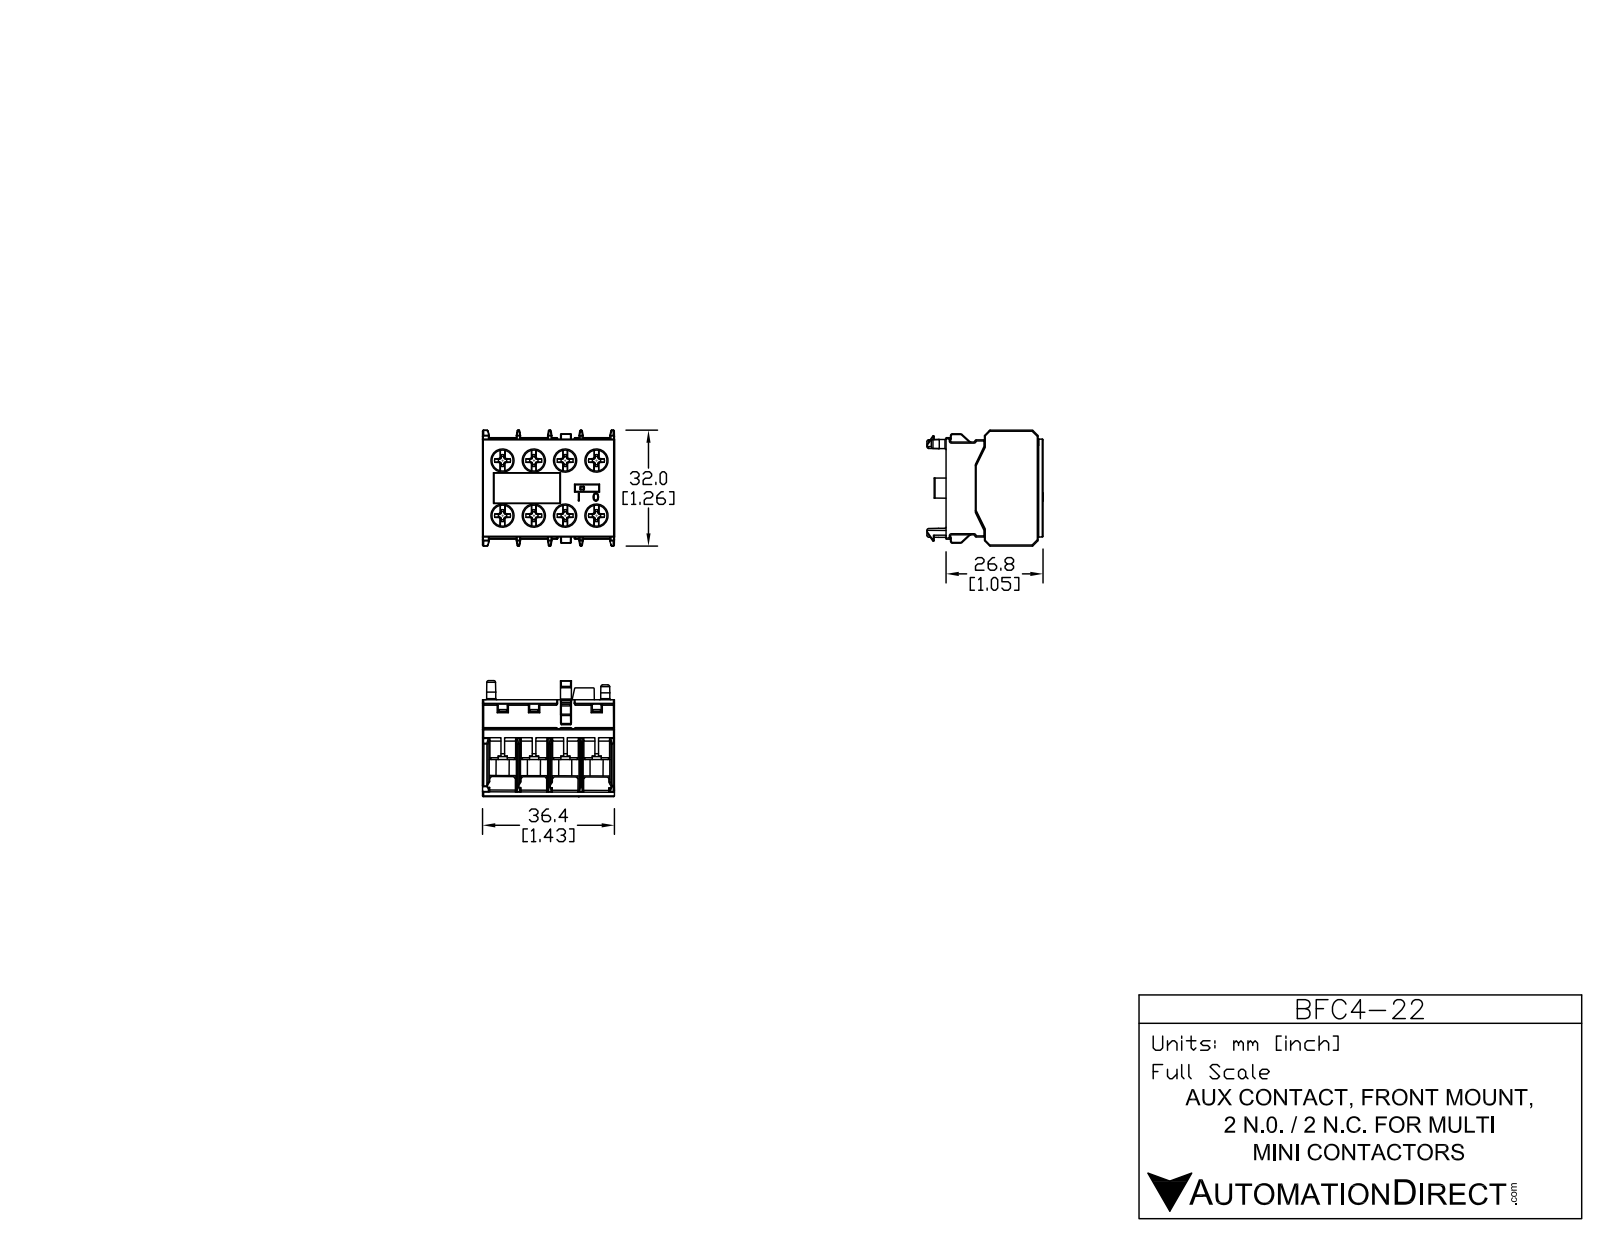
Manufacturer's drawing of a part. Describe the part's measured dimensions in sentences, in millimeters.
The part is named "BFC4-22". Its 3-D file was written by "SolidWorks 2013 (AUTOMOTIVE_DESIGN)". It is 20 solids with 761 faces: 593 planar, 168 cylindrical and 0 other. Overall it measures 36.5 by 32.23 by 32 millimeters. Its volume is 16 423 cubic millimeters and its surface area 17 387 square millimeters. Round holes: 8 of diameter 6. Round bosses or shafts: 8 of diameter 5, 8 of diameter 3, 3 of diameter 2.75. Partial cylindrical surfaces (rounded edges, fillets, slot ends): 8 of radius 0.5, 8 of radius 4.52, 6 of radius 0.3, 4 of radius 0.25, 2 of radius 0.14, 2 of radius 0.19, 2 of radius 0.2. The main face-to-face distances are 1.25, 17.25, 8.63, 16, 8.62, 25.88, 7.38, 18.5, 9.88, 7.37. The hole center spacings are 8.63, 15, 17.25, 17.31, 22.86, 8.62, 17.3, 25.88.
